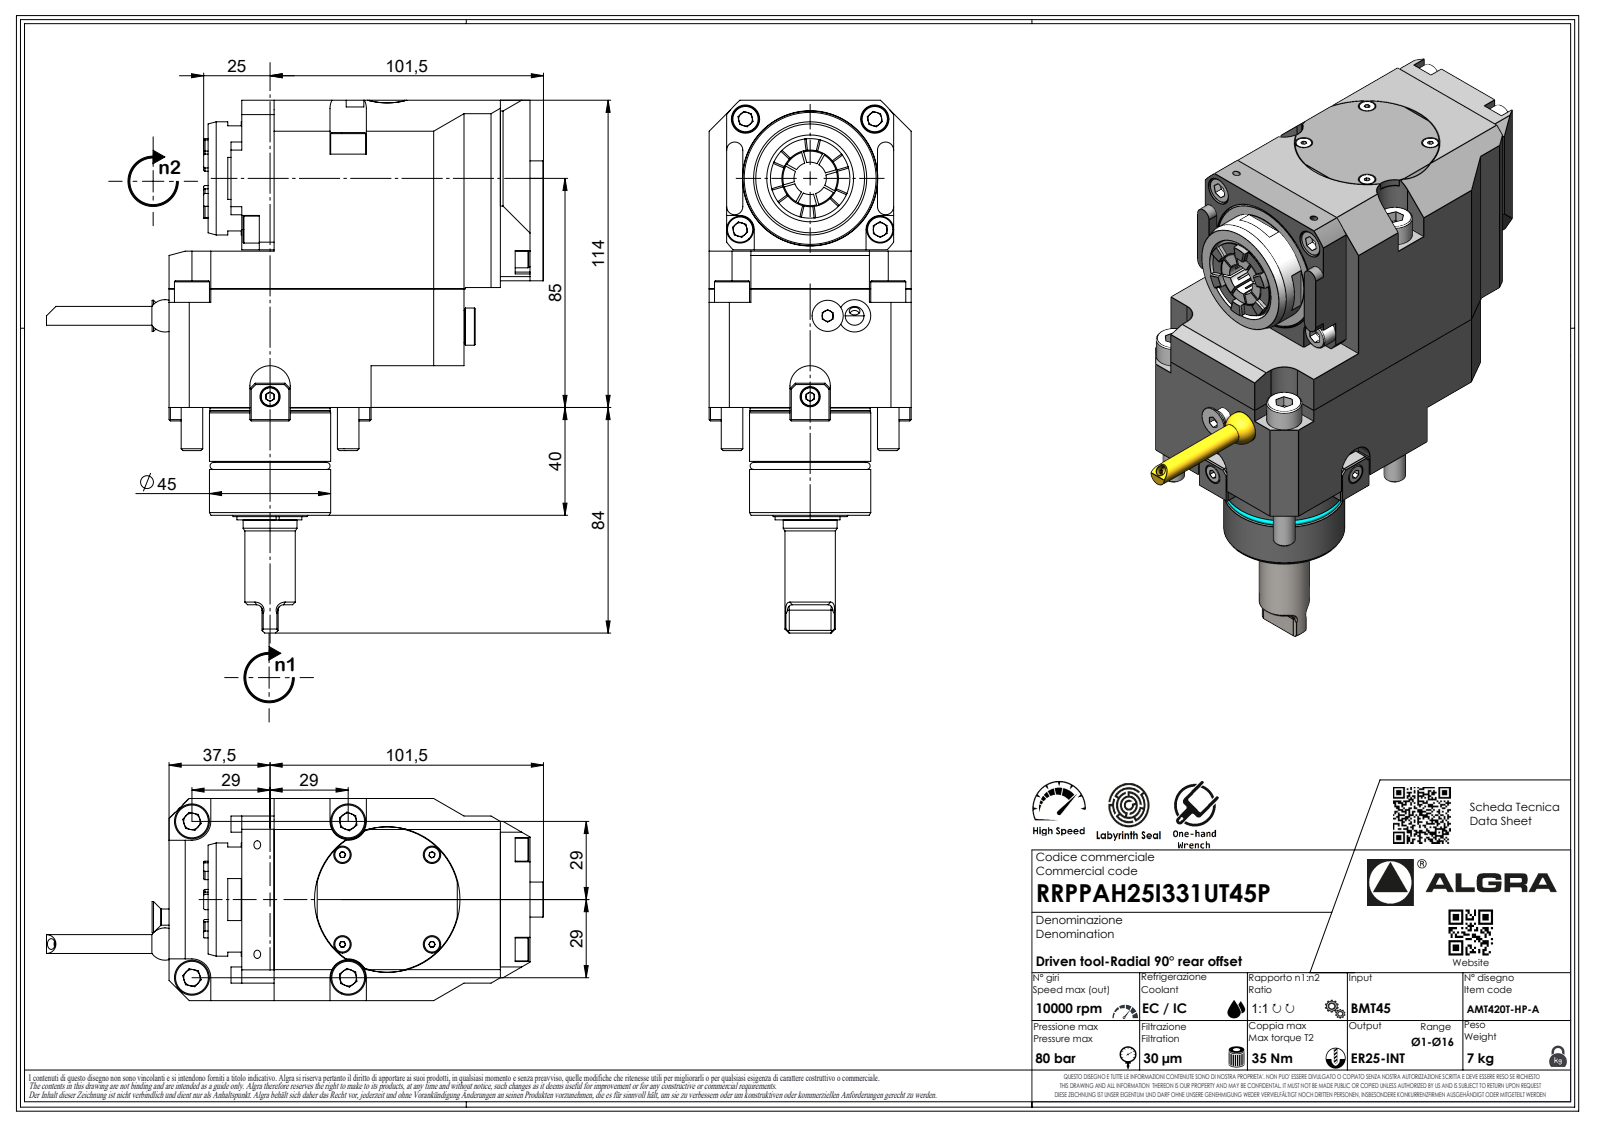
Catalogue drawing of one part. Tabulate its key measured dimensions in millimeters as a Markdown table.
| quantity | value |
| --- | --- |
| part name | RRPPAH25I331UT45P |
| STEP written by | SolidWorks 2023 (AUTOMOTIVE_DESIGN) |
| units | millimeters |
| bodies | 1 solid, 660 faces (429 planar, 103 cylindrical, 128 other) |
| overall size | 196.5 × 184.5 × 75 |
| volume | 937 074 mm³ |
| surface area | 75 781 mm² |
| round holes (diameter × count) | 2.1 × 1, 4 × 1 |
| round bosses / shafts (diameter × count) | 13 × 4, 8 × 4, 45 × 1, 44.6 × 1, 42.4 × 1, 42 × 1, 20 × 1, 19 × 1 |
| partial cylindrical surfaces (radius × count) | 35 × 10, 0.33 × 7, 0.52 × 7, 2 × 7, 3.7 × 7, 3 × 4, 4.5 × 4, 5.25 × 2 |
| main face-to-face distances | 75, 114, 15.5, 98.5, 24.5, 6.5, 68.5, 56, 42.5, 58 |
